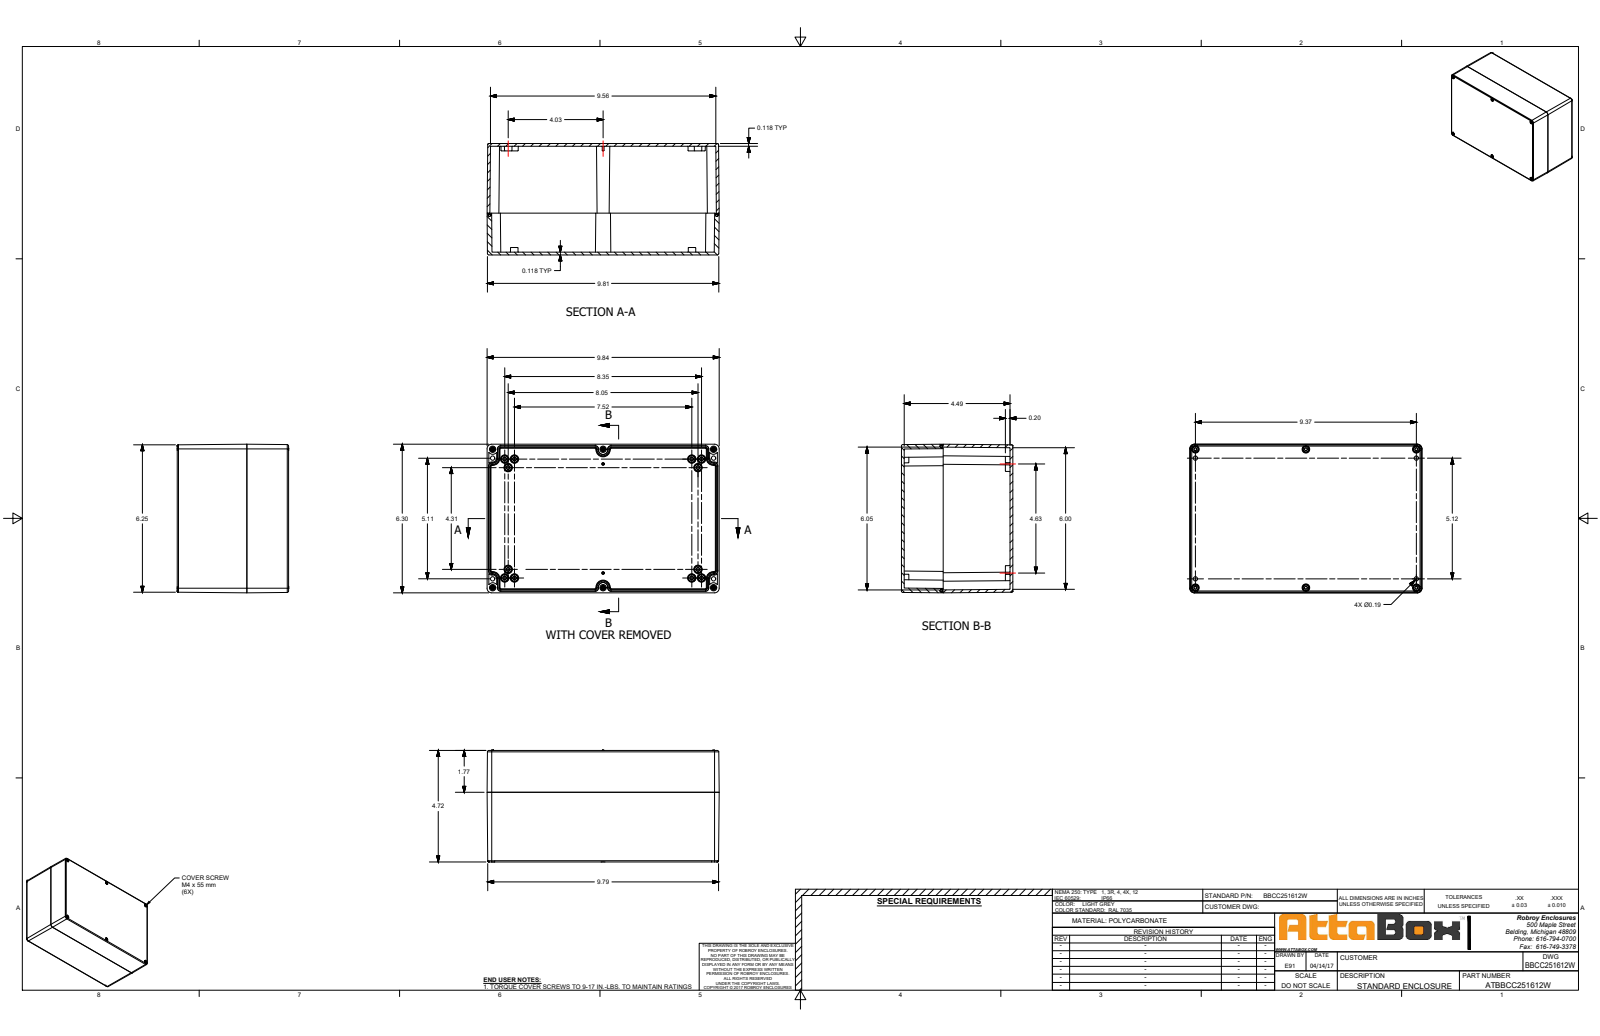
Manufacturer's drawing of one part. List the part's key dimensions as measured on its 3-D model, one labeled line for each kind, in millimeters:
Part name (STEP PRODUCT): BBCC251612W
STEP written by: SolidWorks 2018 (AUTOMOTIVE_DESIGN)
Units: millimetres
Bodies: 15 solids, 2425 faces (901 planar, 588 cylindrical, 936 other)
Overall size (bounding box): 250 × 160 × 120
Volume: 628 600 mm³ · Surface area: 400 200 mm²
Round holes (diameter × count): ⌀3.3 ×6, ⌀4.5 ×6, ⌀4.9 ×6, ⌀5.1 ×6, ⌀7 ×6, ⌀7.2 ×6, ⌀8.2 ×6, ⌀4.7 ×4
Round bosses / shafts (diameter × count): ⌀6.8 ×6, ⌀4.4 ×6, ⌀4 ×6, ⌀3.3 ×6
Partial cylindrical surfaces — rounded edges, fillets, slot ends (radius × count): R1.2 ×40, R1 ×20, R1.5 ×16, R4.2 ×16, R0.1 ×12, R0.5 ×10, R2.6 ×6, R3.1 ×6
Main face-to-face distances: 3, 117, 120, 114, 3.1, 156.8, 160, 155.2, 4.7, 152.1
Hole centre spacings: 9.5, 119, 119.4, 139.5, 183.4, 190.7, 238, 238.2
